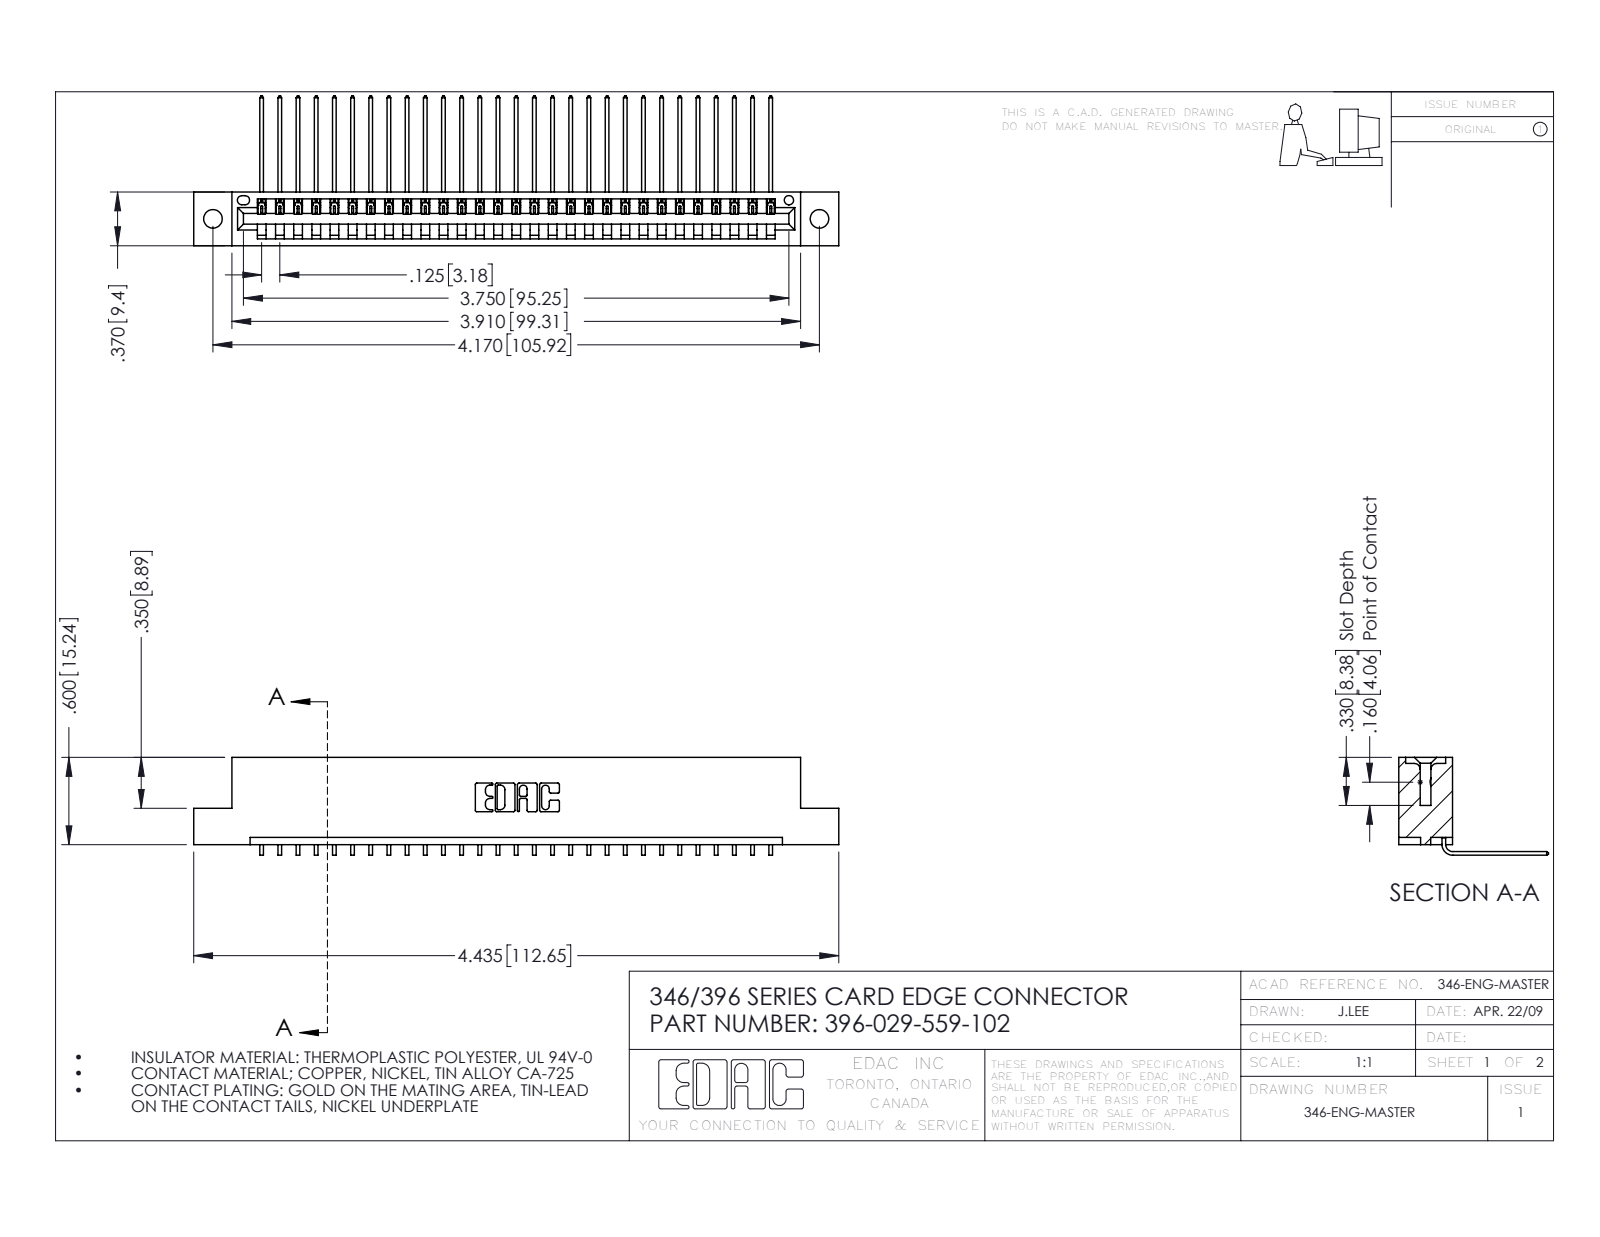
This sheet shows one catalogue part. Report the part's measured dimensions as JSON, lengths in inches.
{"part_name": "396-029-559-102; 345-292-001_558 559 Tail - 1; 346 Part_Flush Mounting Lugs - 0.128 Dia", "step_written_by": "SolidWorks 2016 (CONFIG_CONTROL_DESIGN)", "units": "inches", "bodies": {"solids": 30, "faces": 1862, "planar": 1294, "cylindrical": 568, "other": 0}, "overall_size": [4.435, 1.03, 0.673], "volume_in3": 0.656, "surface_area_in2": 21.09, "round_holes": [[0.128, 2], [0.064, 1]], "partial_cylinders_radius": [[0.006, 58], [0.01, 22], [0.007, 6], [0.031, 6], [0.026, 3], [0.031, 2], [0.04, 2], [0.014, 1]], "face_to_face_distances": [0.048, 0.322, 0.37, 0.25, 0.072, 0.025, 0.298, 0.148, 0.222, 0.1], "hole_center_spacings": [0.246, 3.962, 4.17]}
